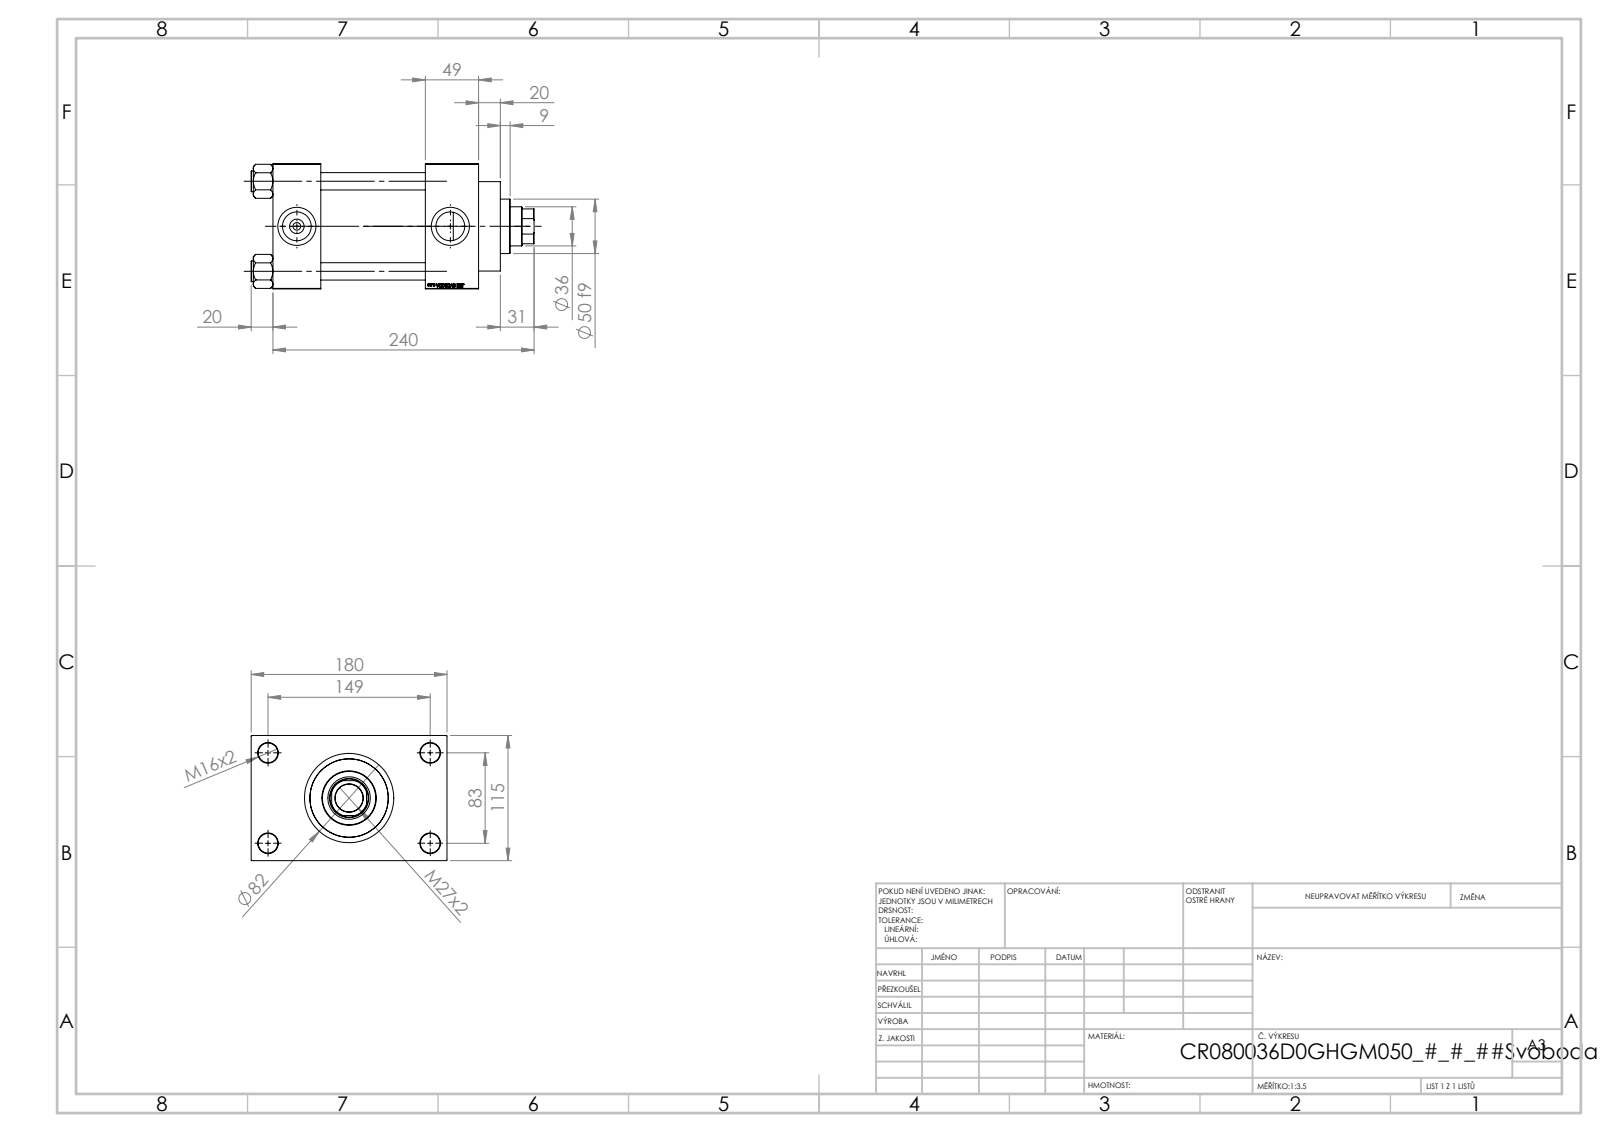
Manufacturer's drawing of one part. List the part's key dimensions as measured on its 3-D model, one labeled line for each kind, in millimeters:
Part name (STEP PRODUCT): V215CR_D_Body; V215CR_D_TYCINKA; NUT_M5_D; V215_VC_A (+1 more)
STEP written by: SolidWorks 2019 (CONFIG_CONTROL_DESIGN)
Units: millimetres
Bodies: 11 solids, 1151 faces (545 planar, 88 cylindrical, 518 other)
Overall size (bounding box): 260 × 180 × 115
Volume: 2 058 000 mm³ · Surface area: 321 664 mm²
Round holes (diameter × count): ⌀16 ×4, ⌀18 ×4, ⌀7 ×2, ⌀26.44 ×2, ⌀35 ×2, ⌀25.5 ×1, ⌀36 ×1, ⌀39 ×1, ⌀61 ×1, ⌀72 ×1, ⌀80 ×1
Round bosses / shafts (diameter × count): ⌀19 ×4, ⌀86 ×1, ⌀82 ×1, ⌀50 ×1
Partial cylindrical surfaces — rounded edges, fillets, slot ends (radius × count): R17.5 ×1
Main face-to-face distances: 115, 96, 145, 49, 44, 140, 189, 32.5, 147.5, 180
Hole centre spacings: 33.15, 58.48, 82.7, 85.28, 89.24, 115.85, 142.43, 83
